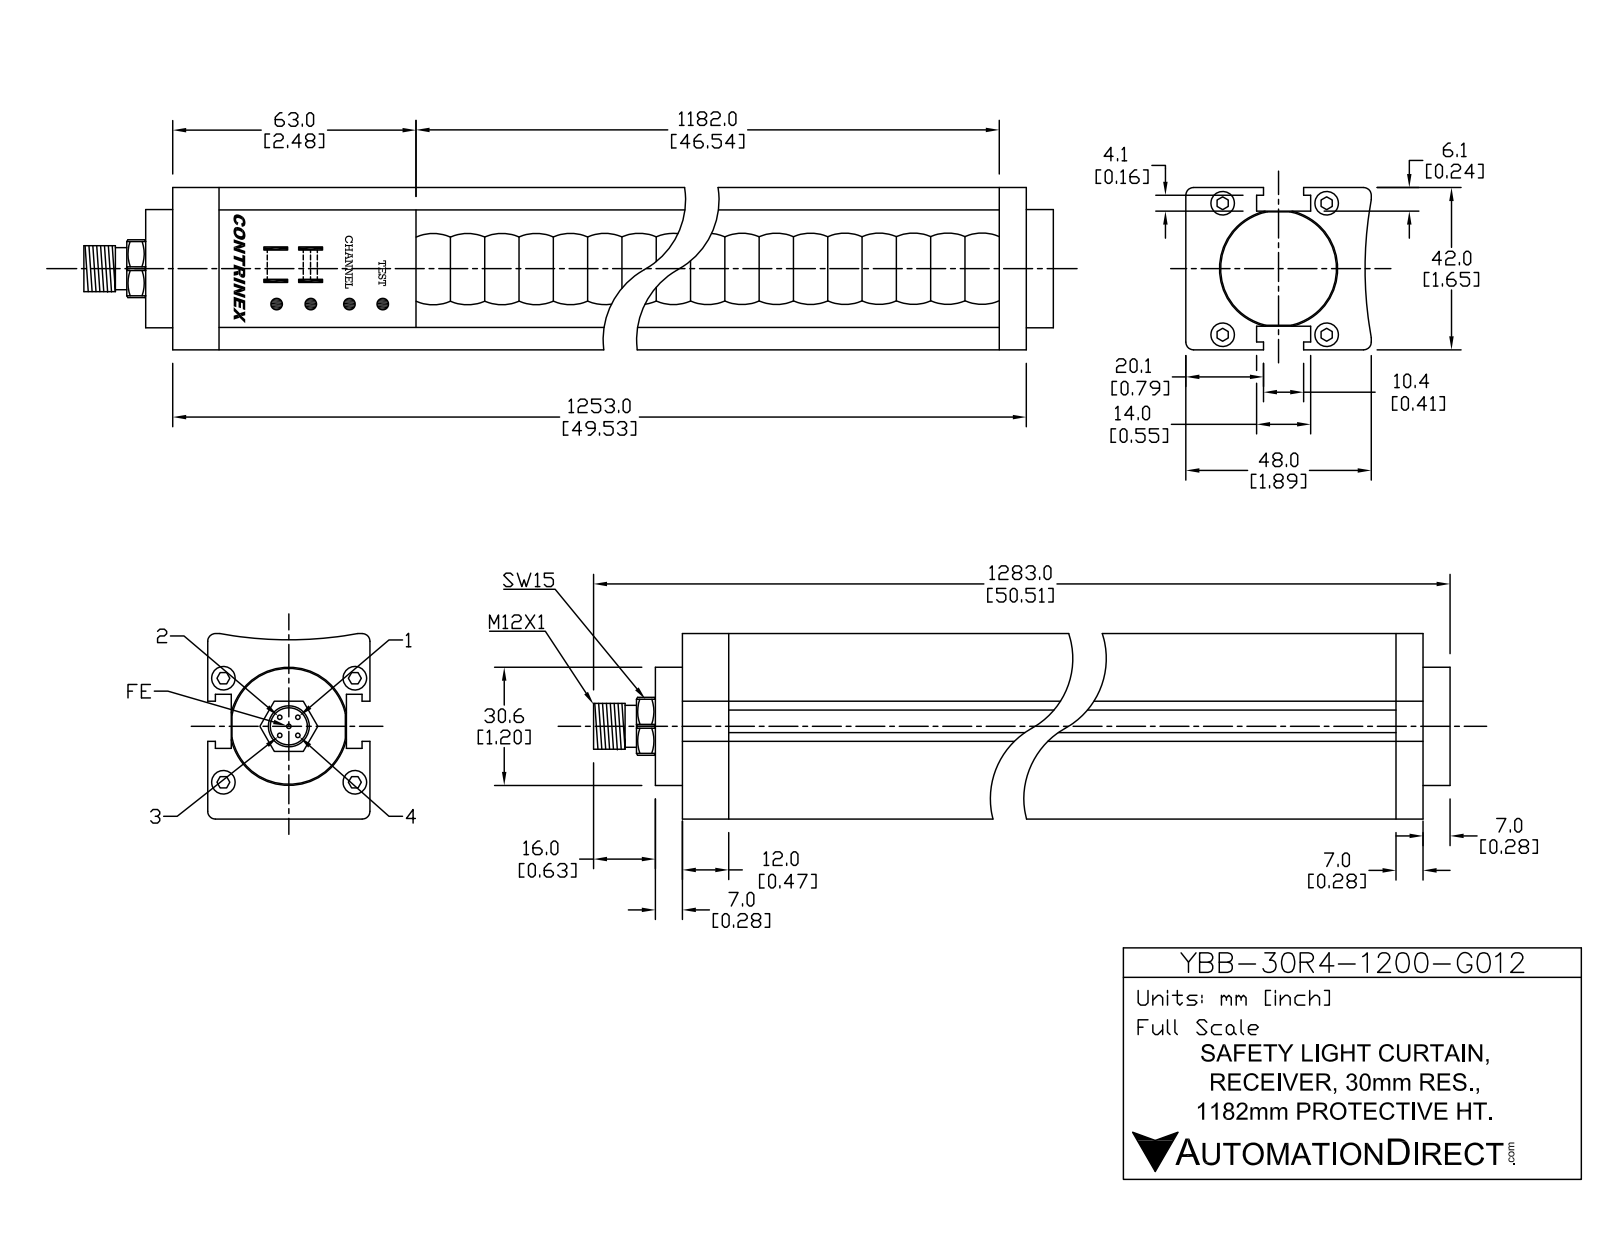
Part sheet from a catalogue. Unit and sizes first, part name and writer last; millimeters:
Units: millimetres
Overall size (bounding box): 1283 × 48 × 42
Round holes (diameter × count): ⌀6 ×4, ⌀8.5 ×1, ⌀32 ×1
Round bosses / shafts (diameter × count): ⌀1 ×5, ⌀5.5 ×4, ⌀30.6 ×1, ⌀12 ×1, ⌀10.5 ×1
Partial cylindrical surfaces — rounded edges, fillets, slot ends (radius × count): R1 ×48, R0.5 ×4, R0.55 ×2, R8.2 ×1, R100 ×1
Main face-to-face distances: 6.3, 35.7, 42, 29.4, 14, 17.2, 31.2, 15.7, 29.7, 46.9
Hole centre spacings: 21.04, 22.34, 26.9, 34, 43.35
Volume: 2 253 000 mm³ · Surface area: 284 832 mm²
Bodies: 19 solids, 440 faces (208 planar, 168 cylindrical, 64 other)
Part name (STEP PRODUCT): YBB-30R4-1200-G012
STEP written by: SolidWorks 2016 (AUTOMOTIVE_DESIGN)
